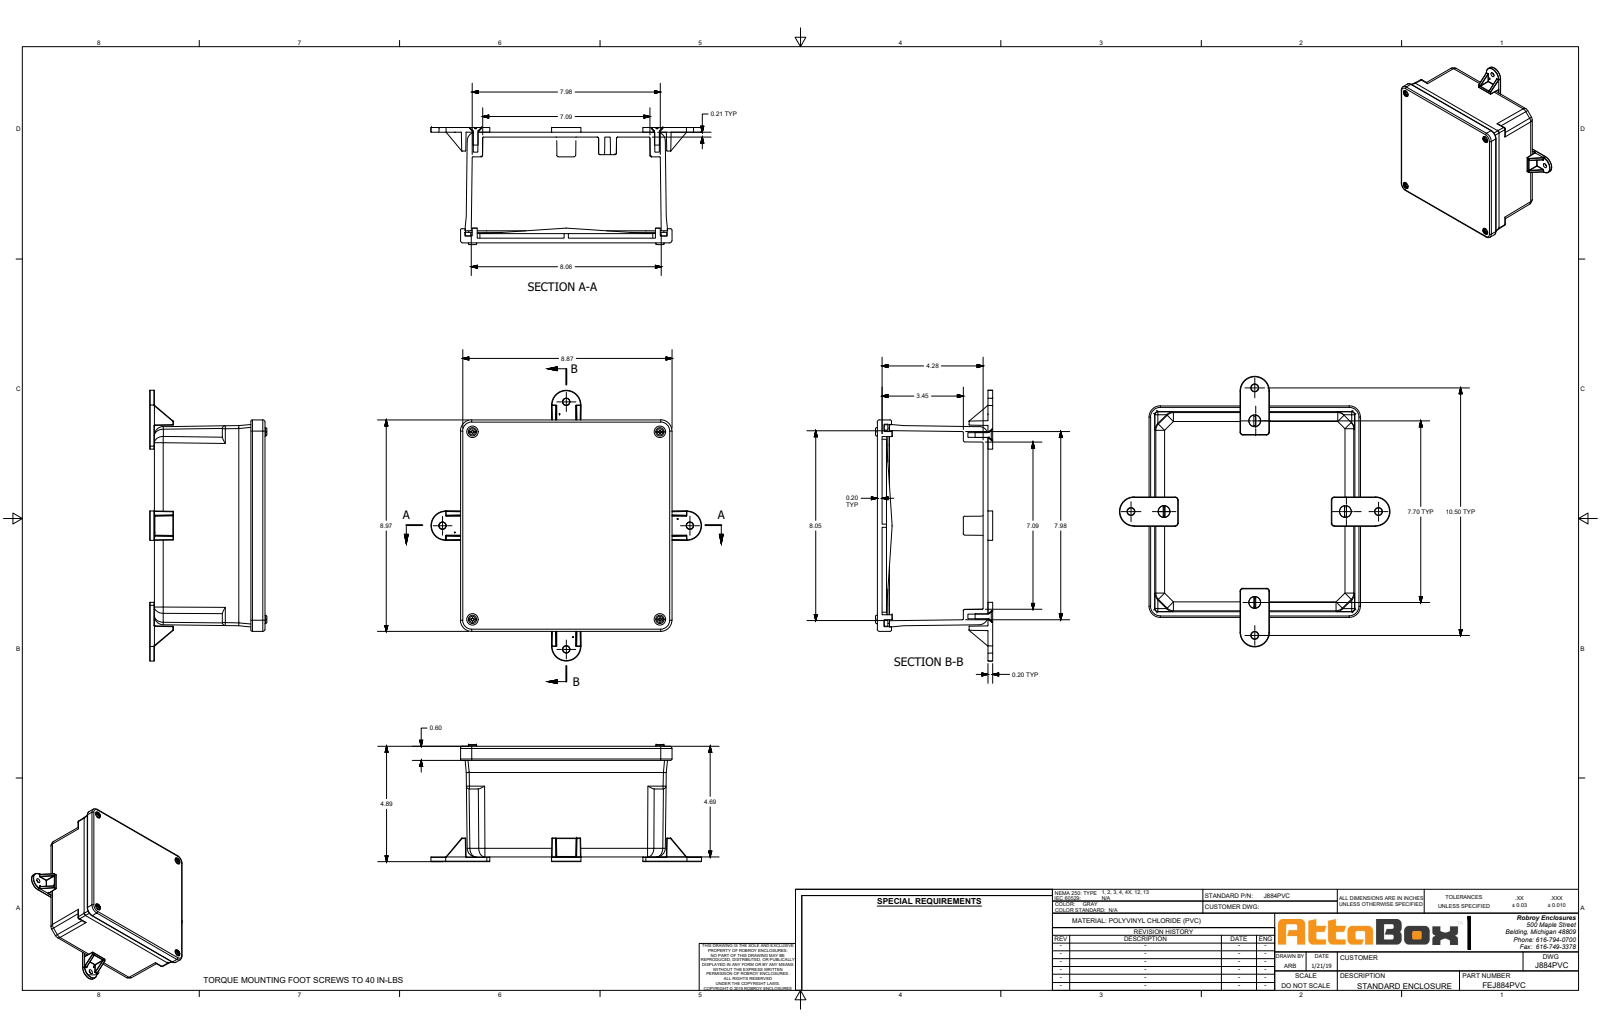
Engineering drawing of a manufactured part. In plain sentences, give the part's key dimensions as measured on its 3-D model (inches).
The part is named "J884PVC". Its 3-D file was written by "SolidWorks 2018 (AUTOMOTIVE_DESIGN)". It is 19 solids with 1001 faces: 443 planar, 338 cylindrical and 220 other. Overall it measures 11.475 by 11.475 by 4.968 inches. Its volume is 71.53 cubic inches and its surface area 693.8 square inches. Round holes: 8 of diameter 0.2, 4 of diameter 0.13, 4 of diameter 0.25, 4 of diameter 0.265, 4 of diameter 0.276, 4 of diameter 0.31, 4 of diameter 0.39, 4 of diameter 0.47, 4 of diameter 0.48, 4 of diameter 0.5. Round bosses or shafts: 4 of diameter 0.354, 4 of diameter 0.325, 4 of diameter 0.187, 4 of diameter 0.177. Partial cylindrical surfaces (rounded edges, fillets, slot ends): 76 of radius 0.02, 20 of radius 0.025, 20 of radius 0.03, 20 of radius 0.125, 16 of radius 0.005, 16 of radius 0.375, 12 of radius 0.094, 10 of radius 0.25. The main face-to-face distances are 4.692, 0.2, 0.21, 4.482, 4.492, 4.282, 0.22, 0.22, 0.29, 4.402. The hole center spacings are 7.95, 8.774, 3.977, 3.977, 7.906, 11.243, 8.775, 0.044.
